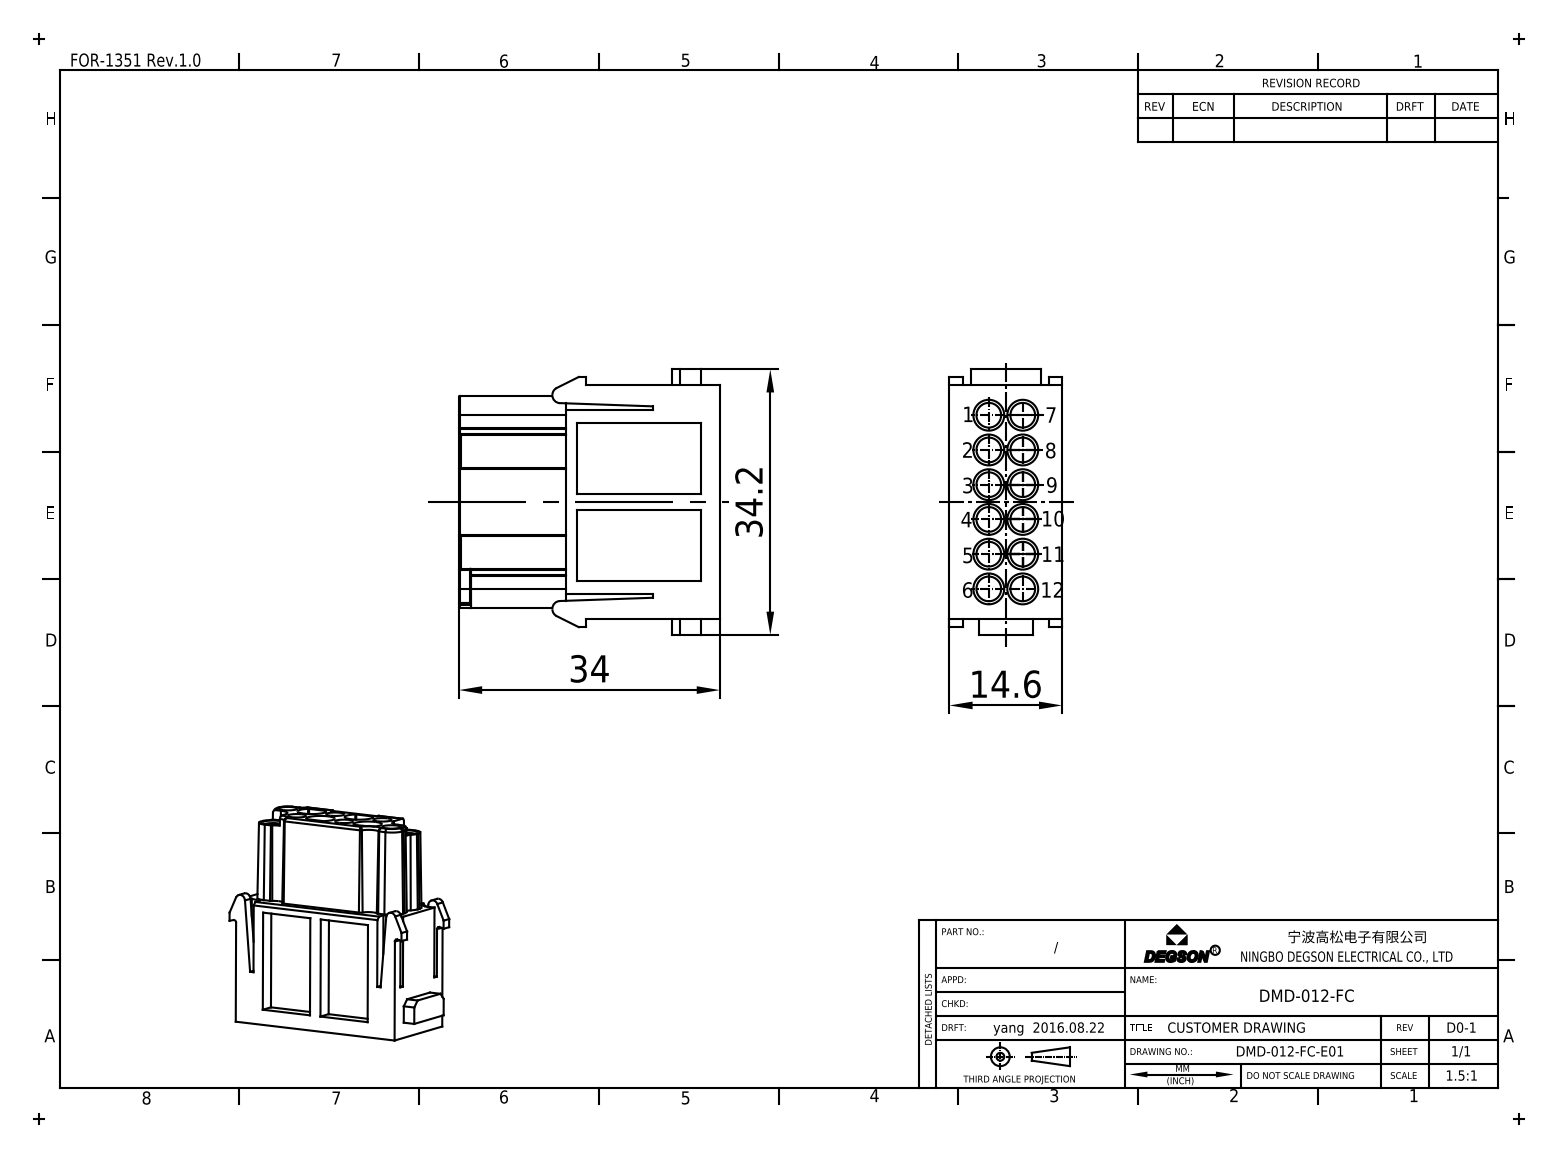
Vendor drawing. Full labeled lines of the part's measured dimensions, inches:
Part name (STEP PRODUCT): DMD-012-FC-Z1-00AH_T0
STEP written by: CREO PARAMETRIC BY PTC INC, 2014350 (CONFIG_CONTROL_DESIGN)
Units: inches
Bodies: 1 solid, 350 faces (139 planar, 118 cylindrical, 93 other)
Overall size (bounding box): 1.35 × 1.339 × 0.575
Volume: 0.409 in³ · Surface area: 13.31 in²
Round holes (diameter × count): ⌀0.102 ×12, ⌀0.122 ×12, ⌀0.142 ×12, ⌀0.157 ×12
Partial cylindrical surfaces — rounded edges, fillets, slot ends (radius × count): R0.008 ×8, R0.02 ×6, R0.091 ×6, R0.065 ×1
Main face-to-face distances: 0.098, 0.476, 0.378, 0.433, 0.079, 0.787, 0.636, 0.203, 1.069, 0.575
Hole centre spacings: 0.177, 0.25, 0.354, 0.396, 0.531, 0.56, 0.709, 0.73
